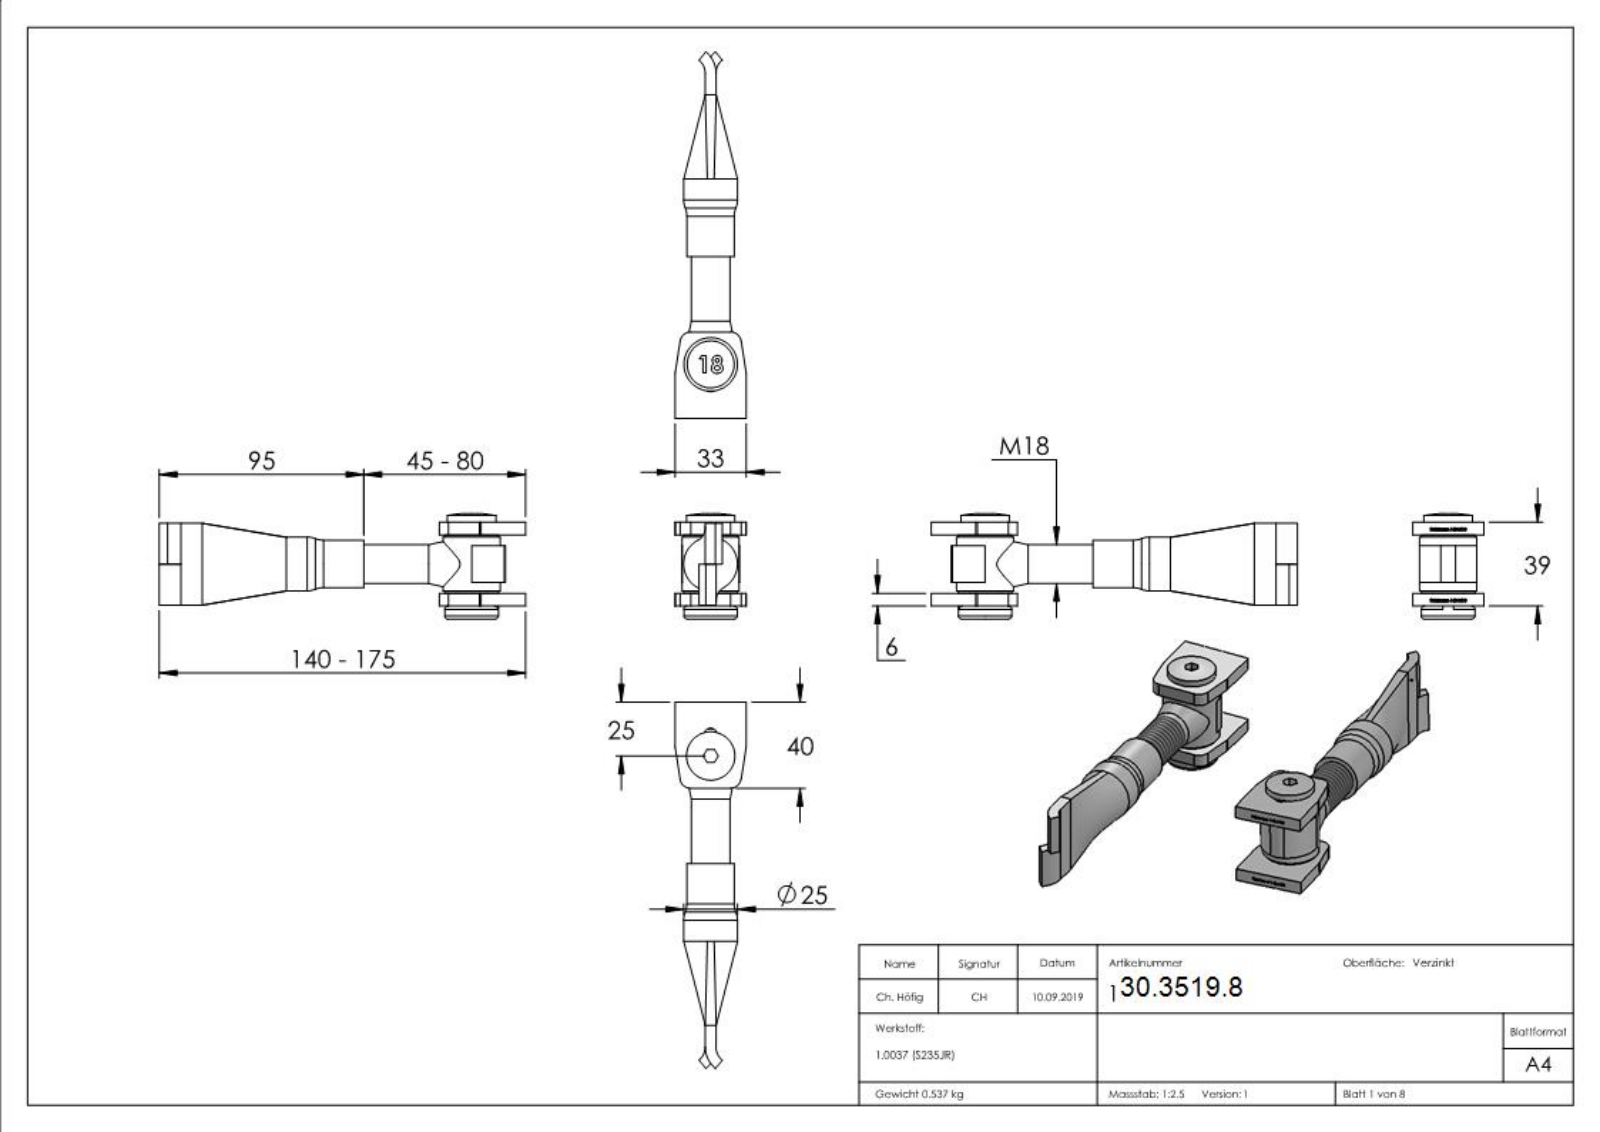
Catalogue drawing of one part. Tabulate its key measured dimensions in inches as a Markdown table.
| quantity | value |
| --- | --- |
| part name | 140-MXX Teil5_140-M18 Teil5; 140-MXX Teil2_140-M18 Teil2; 140-M18; 140-MXX Teil6_140-M18 Teil6 (+3 more) |
| STEP written by | SolidWorks 2015 (CONFIG_CONTROL_DESIGN) |
| units | inches |
| bodies | 8 solids, 559 faces (303 planar, 56 cylindrical, 200 other) |
| overall size | 6.693 × 1.93 × 1.299 |
| volume | 4.231 in³ |
| surface area | 50.54 in² |
| round holes (diameter × count) | 0.591 × 2, 0.268 × 1, 0.354 × 1, 0.587 × 1, 0.61 × 1, 0.63 × 1 |
| round bosses / shafts (diameter × count) | 0.984 × 2, 1.043 × 1, 0.976 × 1, 0.886 × 1, 0.866 × 1, 0.709 × 1, 0.571 × 1, 0.315 × 1 |
| partial cylindrical surfaces (radius × count) | 0.197 × 4, 0.312 × 2, 0.509 × 2, 0.591 × 2, 0.122 × 1, 0.394 × 1 |
| main face-to-face distances | 0.236, 1.299, 1.535, 1.26, 0.276, 0.039, 1.024, 1.063, 0.984, 0.24 |
